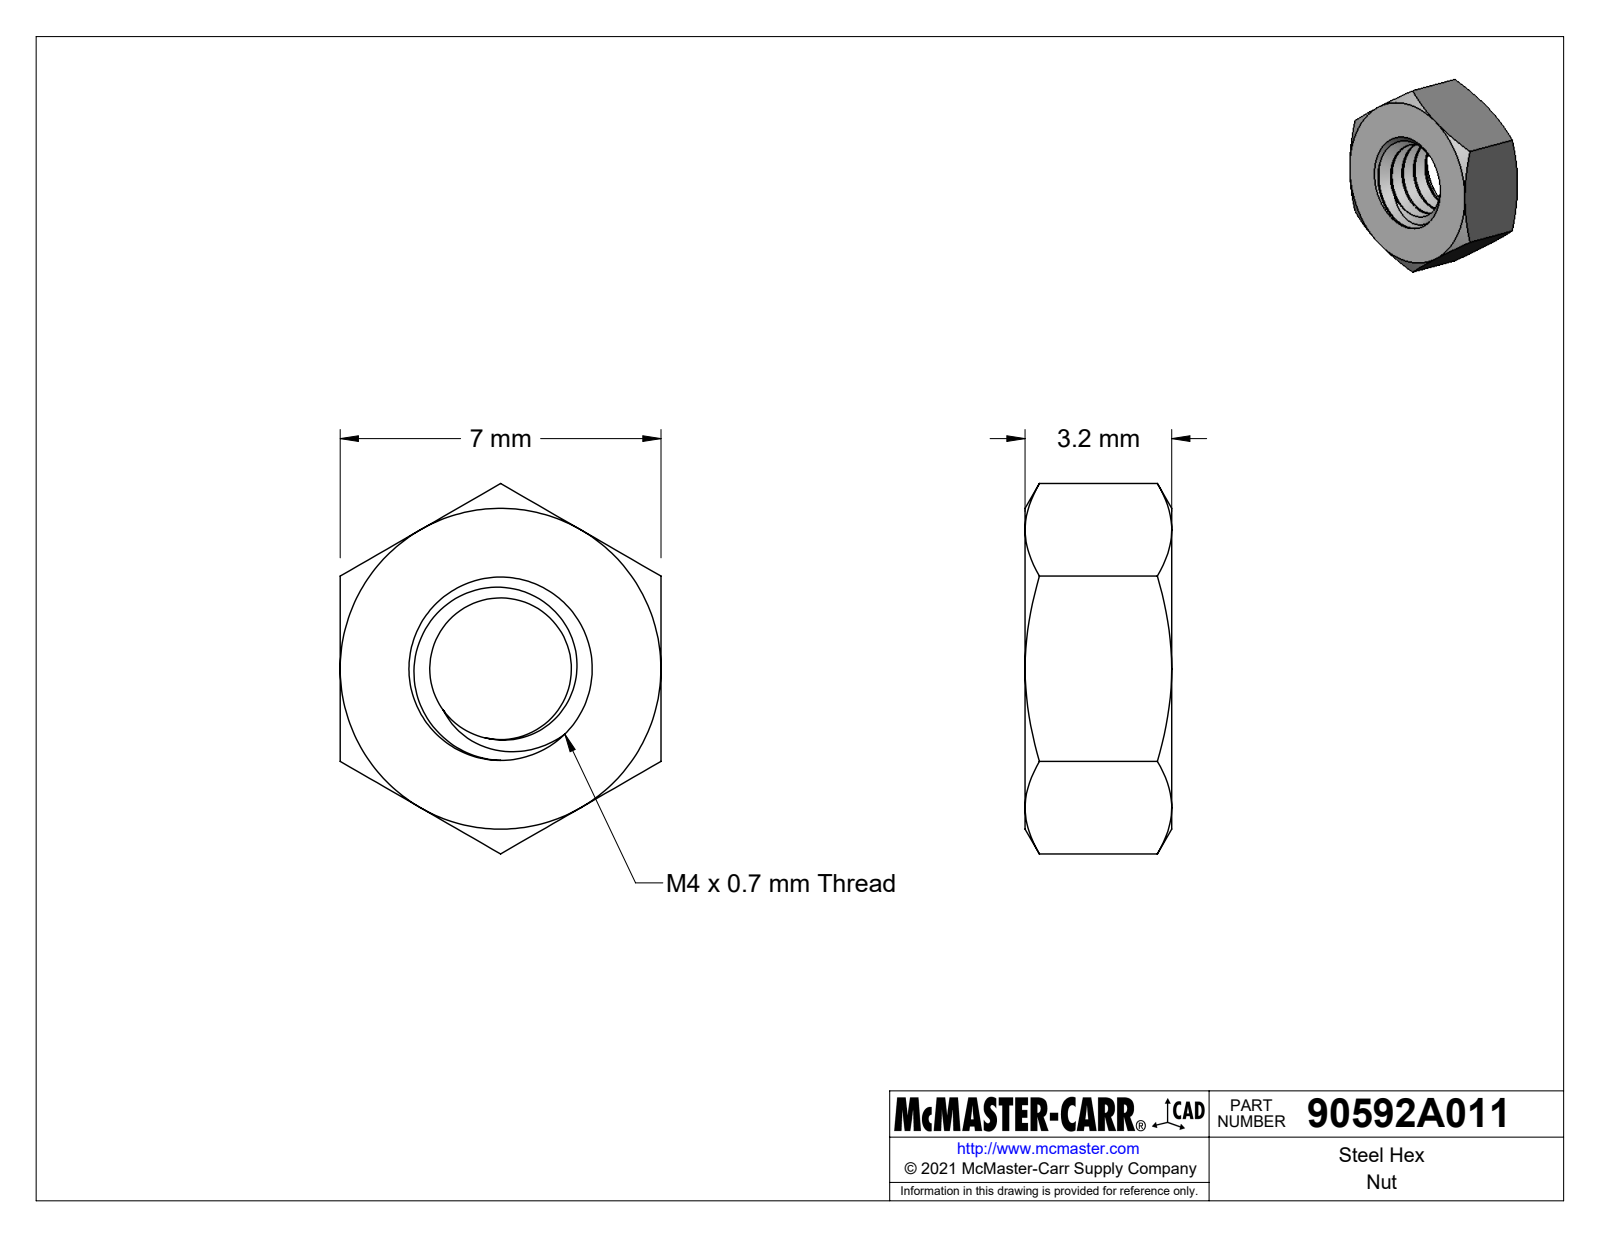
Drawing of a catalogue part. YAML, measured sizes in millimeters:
part_name: "90592A011_Steel Hex Nut"
step_written_by: "SolidWorks 2017 (CONFIG_CONTROL_DESIGN)"
units: millimeters
bodies: {solids: 1, faces: 42, planar: 8, cylindrical: 11, other: 23}
overall_size: [8.08, 7, 3.2]
volume: 102
surface_area: 195
round_holes:
  - {diameter: 4, count: 1}
face_to_face_distances: [7, 3.2]
